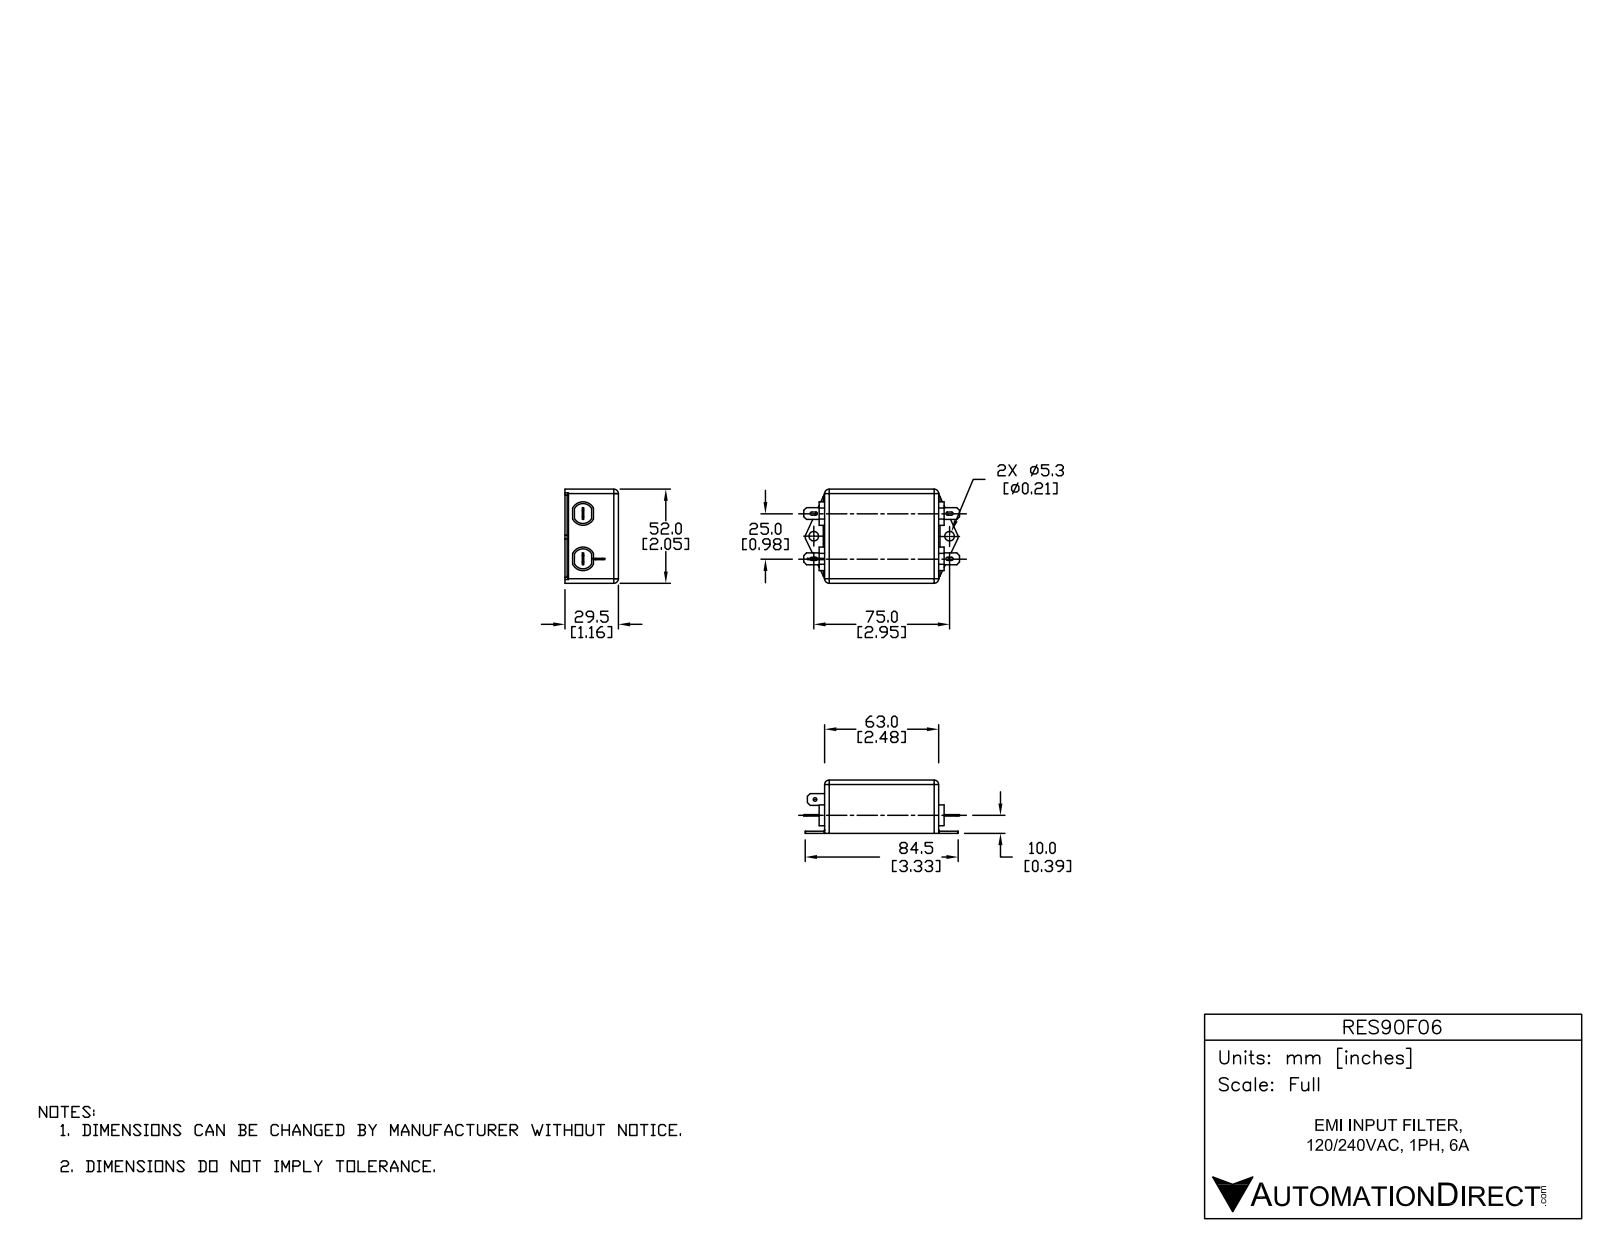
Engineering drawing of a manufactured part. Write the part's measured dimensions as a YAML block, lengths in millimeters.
part_name: "RES90F06"
step_written_by: "SolidWorks 2015 (AUTOMOTIVE_DESIGN)"
units: millimeters
bodies: {solids: 1, faces: 133, planar: 79, cylindrical: 50, other: 4}
overall_size: [86, 52.5, 29.5]
volume: 98907
surface_area: 15385
round_holes:
  - {diameter: 5.3, count: 2}
  - {diameter: 2, count: 1}
partial_cylinders:
  - {radius: 2.5, count: 10}
  - {radius: 0.88, count: 8}
  - {radius: 0.75, count: 2}
  - {radius: 5.5, count: 2}
  - {radius: 6.5, count: 2}
face_to_face_distances: [29.5, 52.5, 63, 1.5, 1.2, 28.3, 64.5, 66, 0.8, 10.4]
hole_center_spacings: [75]
